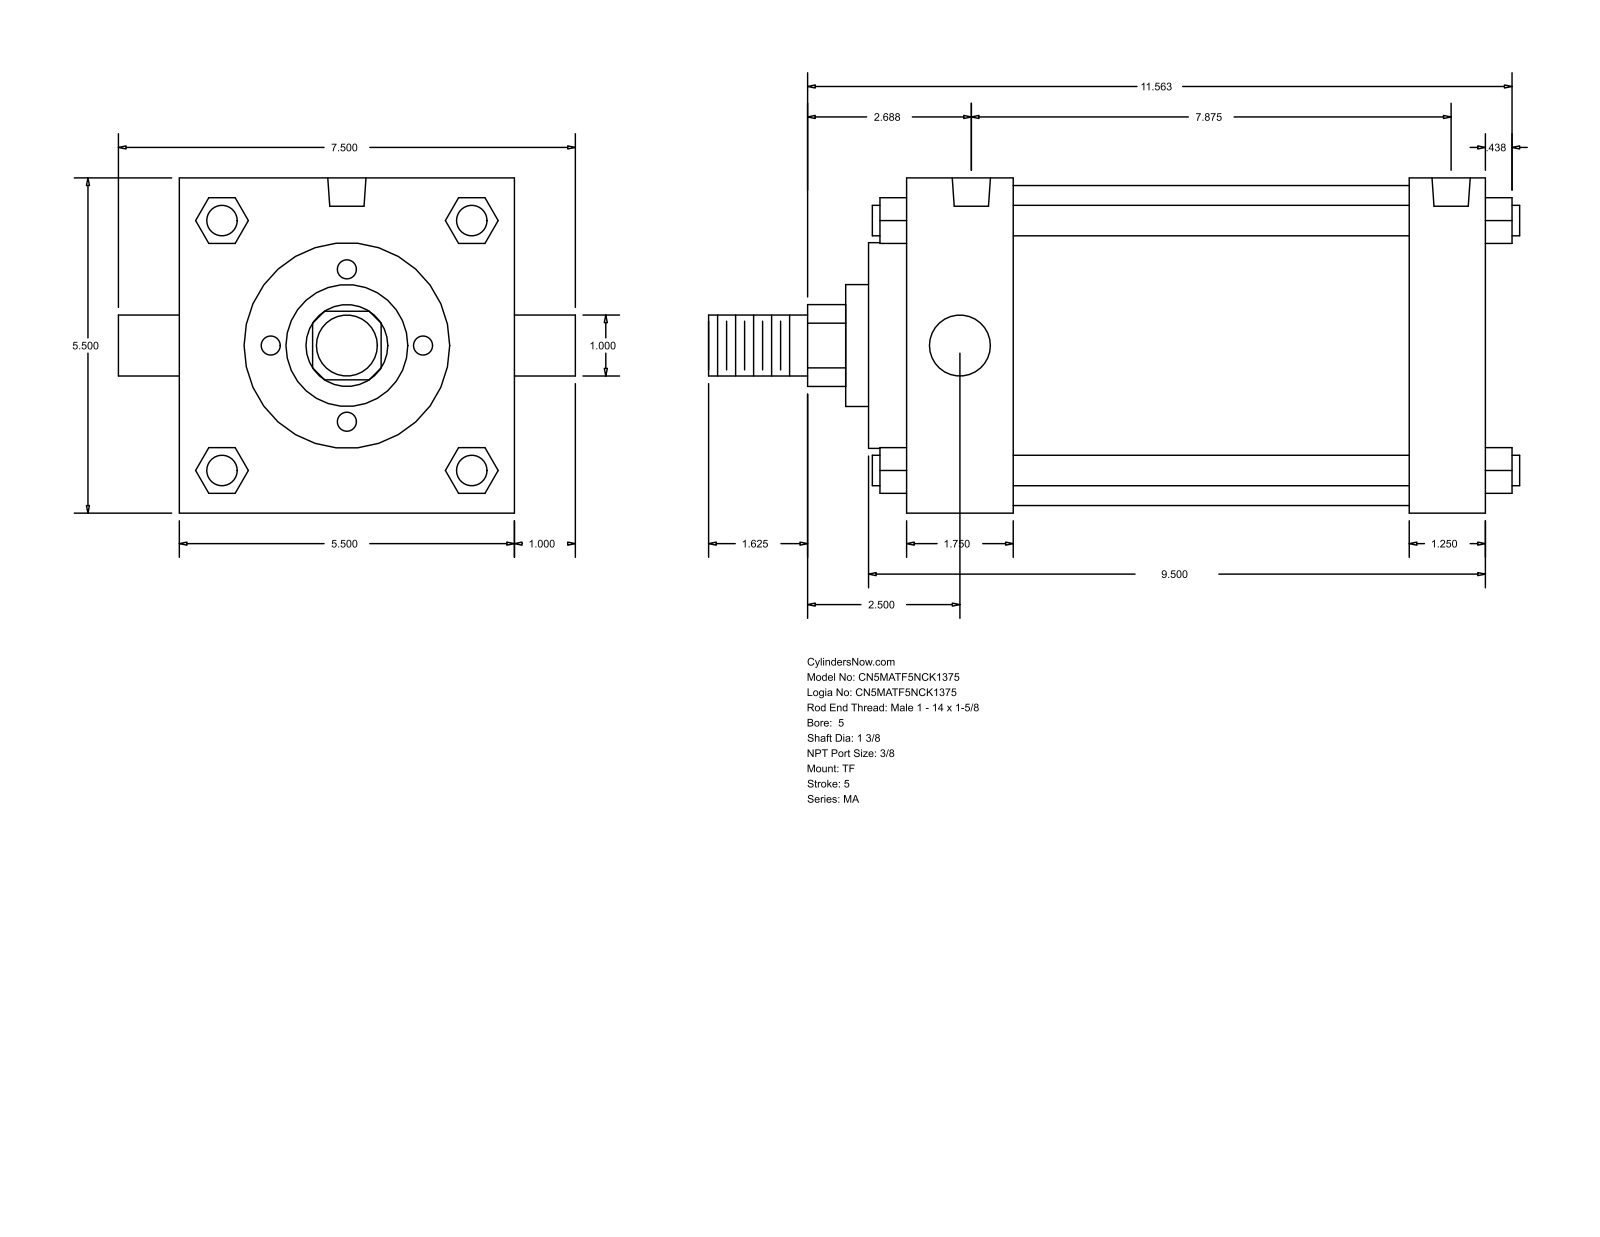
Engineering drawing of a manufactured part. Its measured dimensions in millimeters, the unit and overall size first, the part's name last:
Units: millimetres
Overall size (bounding box): 338.14 × 190.5 × 139.7
Round holes (diameter × count): ⌀11.11 ×3, ⌀15.93 ×2
Round bosses / shafts (diameter × count): ⌀12.7 ×4, ⌀25.4 ×2, ⌀133.35 ×1, ⌀85.72 ×1, ⌀50.8 ×1, ⌀34.92 ×1
Partial cylindrical surfaces — rounded edges, fillets, slot ends (radius × count): R17.06 ×1
Main face-to-face distances: 139.7, 241.3, 165.1, 209.55, 31.75, 44.45, 196.85, 15.87, 60.32, 225.42
Hole centre spacings: 4.77, 195.26, 190.49, 200.03
Bodies: 0 solids, 122 faces (93 planar, 29 cylindrical, 0 other)
Part name (STEP PRODUCT): MA_TF__0500_1.375
STEP written by: GSSL Pune (CONFIG_CONTROL_DESIGN)
